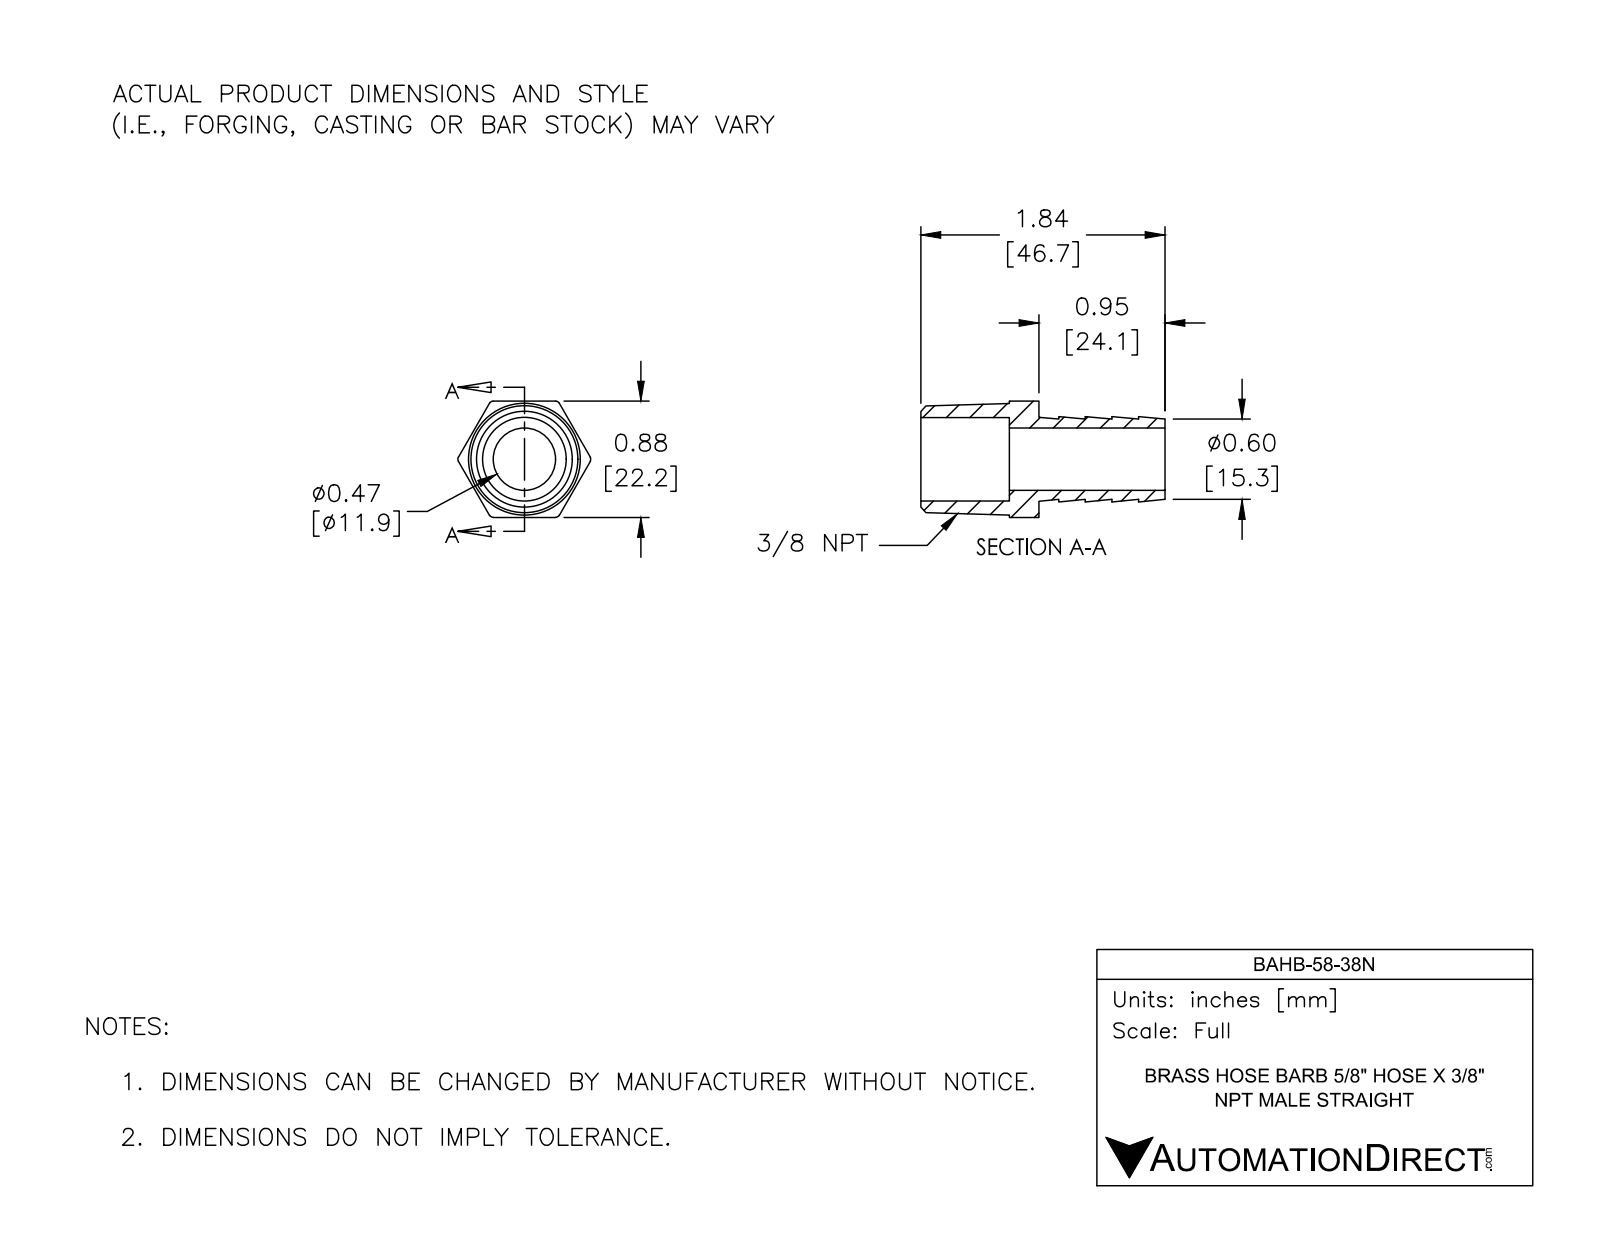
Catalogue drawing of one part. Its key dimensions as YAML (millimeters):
part_name: "BAHB-58-38N"
step_written_by: "SolidWorks 2017 (AUTOMOTIVE_DESIGN)"
units: millimeters
bodies: {solids: 1, faces: 39, planar: 15, cylindrical: 10, other: 14}
overall_size: [46.7, 25.4, 22.2]
volume: 6210
surface_area: 5346
round_holes:
  - {diameter: 11.9, count: 1}
  - {diameter: 16, count: 1}
partial_cylinders:
  - {radius: 0.8, count: 6}
face_to_face_distances: [22.2, 5.7, 5.1, 24.1, 29.7, 10.2, 46.7, 22.6, 16.9, 15.2]
